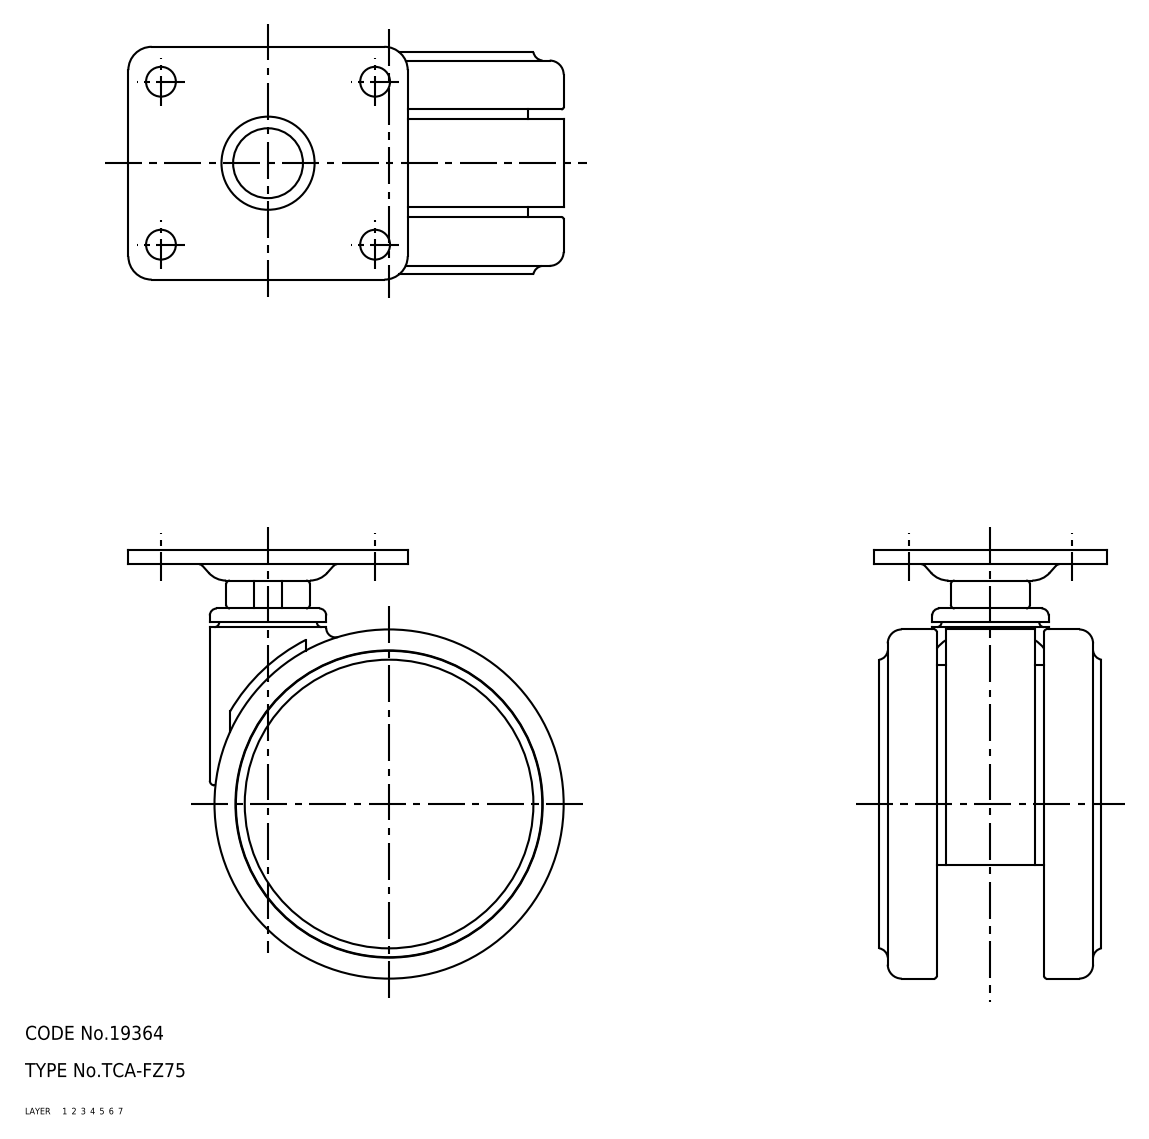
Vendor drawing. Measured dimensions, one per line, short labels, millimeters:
name: caster; TCA-FZ75
written by: SolidWorks 2015 (AUTOMOTIVE_DESIGN)
unit: mm
bodies: 2 solids, 1831 faces (428 planar, 783 cylindrical, 620 other)
size: 93.5 × 92 × 50
volume: 120 349 mm³; area: 74 778 mm²
holes: 4× ⌀6.4, 1× ⌀6.5, 1× ⌀8, 1× ⌀8.1, 1× ⌀10.2, 1× ⌀11, 1× ⌀17, 1× ⌀18.1, 1× ⌀19, 1× ⌀22.6, 1× ⌀59, 1× ⌀63
bosses: 2× ⌀16, 2× ⌀14, 1× ⌀65.8, 1× ⌀54, 1× ⌀26, 1× ⌀25, 1× ⌀10, 1× ⌀8
rounds: 139× R1, 132× R0.3, 127× R0.5, 16× R0.2, 12× R2, 4× R5, 2× R6, 1× R3
face distances: 1.5, 46.2, 3.3, 1.8, 44.4, 42.9, 32.1, 9, 12.3, 35.4
hole spacings: 28.9, 35, 46, 57.8
